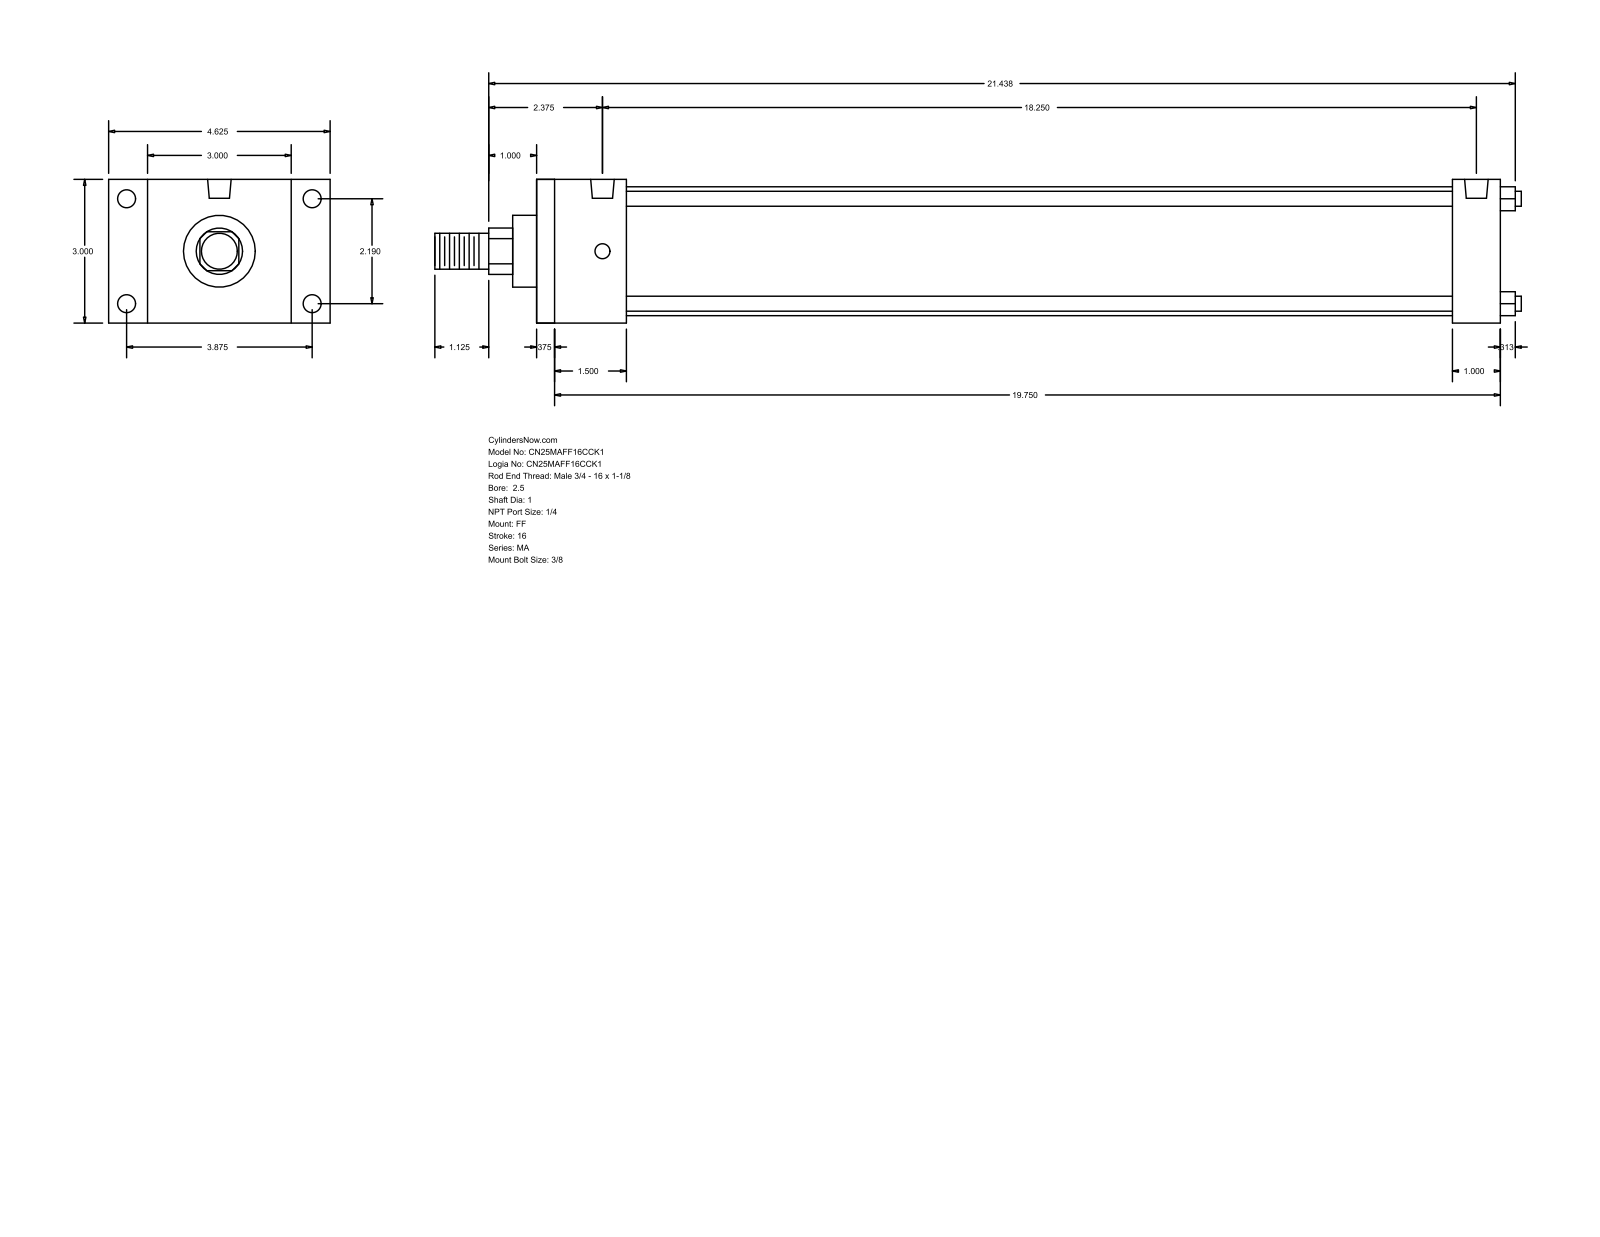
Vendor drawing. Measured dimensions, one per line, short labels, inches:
name: MA_FF__0250_1
written by: GSSL Pune (CONFIG_CONTROL_DESIGN)
unit: in
bodies: 0 solids, 92 faces (64 planar, 28 cylindrical, 0 other)
size: 22.687 × 4.625 × 3
holes: 4× ⌀0.313, 4× ⌀0.375, 2× ⌀0.492
bosses: 4× ⌀0.313, 1× ⌀2.69, 1× ⌀1.5, 1× ⌀1, 1× ⌀0.75
rounds: 1× R0.484
face distances: 3, 20.125, 0.375, 19.75, 1, 1.875, 19.125, 1.5, 18.75, 17.25
hole spacings: 2.19, 3.875, 4.451, 18.25
